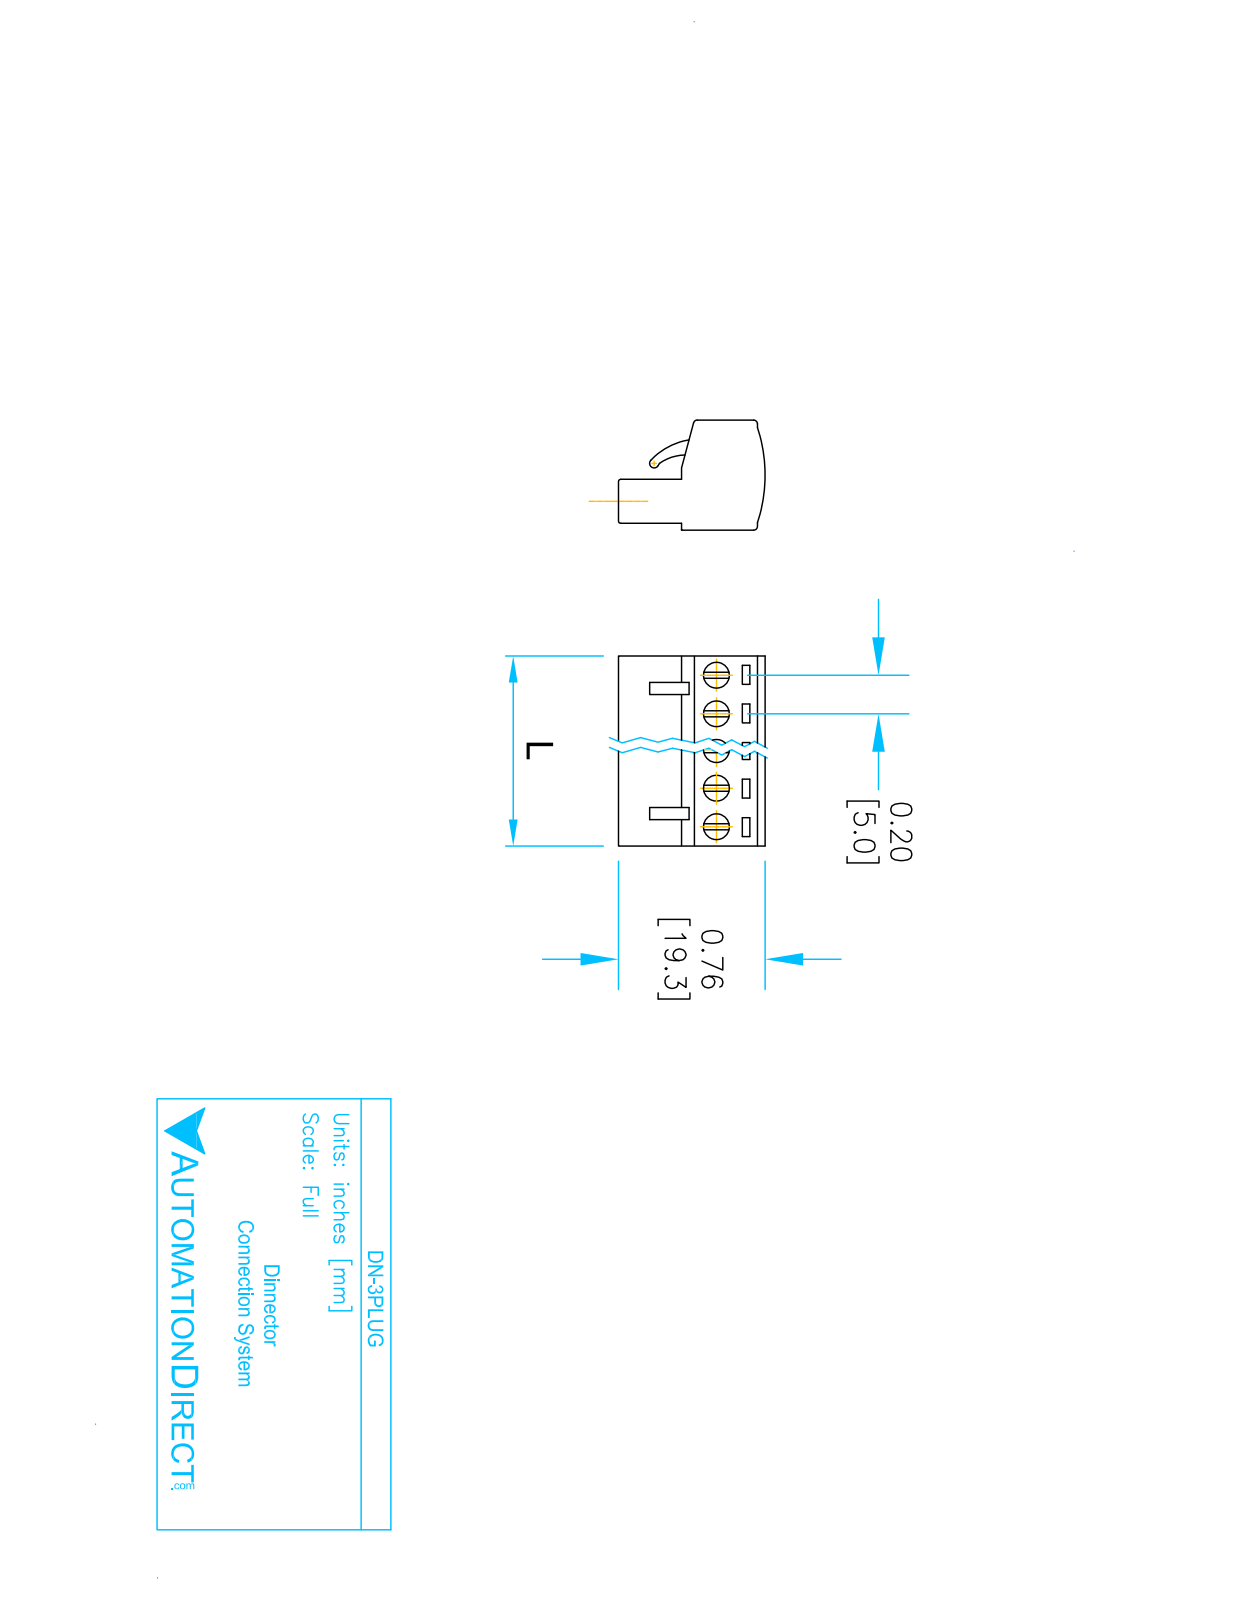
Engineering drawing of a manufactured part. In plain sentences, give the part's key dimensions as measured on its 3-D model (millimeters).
The part is named "49002_S; 49003_S; 49001_S". Its 3-D file was written by "SolidWorks 2013 (AUTOMOTIVE_DESIGN)". It is 2 solids with 263 faces: 181 planar, 67 cylindrical and 15 other. Overall it measures 19.3 by 15.24 by 14.5 millimeters. Its volume is 2 621 cubic millimeters and its surface area 2 480 square millimeters. Round holes: 3 of diameter 1.6, 3 of diameter 2.5, 3 of diameter 3.4, 3 of diameter 3.6. Round bosses or shafts: 3 of diameter 3. Partial cylindrical surfaces (rounded edges, fillets, slot ends): 3 of radius 0.5, 3 of radius 2.9, 2 of radius 0.3, 1 of radius 0.6, 1 of radius 6, 1 of radius 9, 1 of radius 20.03. The main face-to-face distances are 5.08, 10.16, 15.24, 6.7, 1, 14.5, 7.8, 0.79, 4.29, 3.4. The hole center spacings are 5.08, 10.16.
